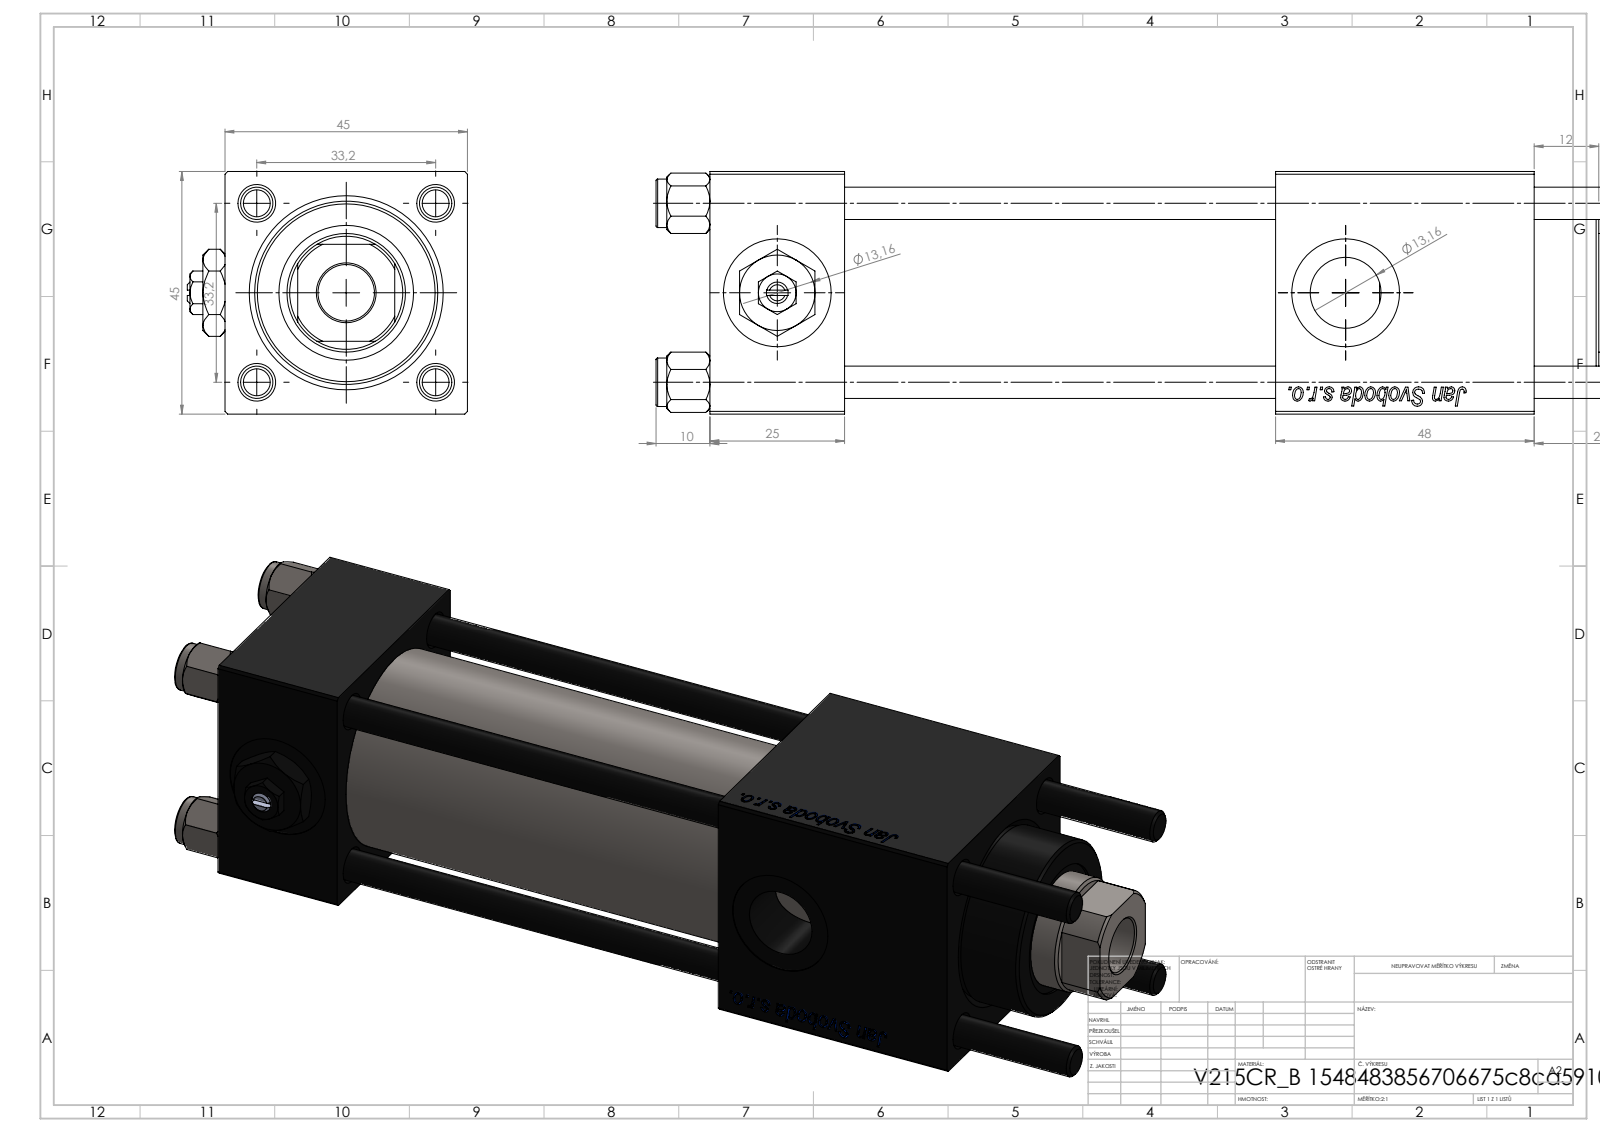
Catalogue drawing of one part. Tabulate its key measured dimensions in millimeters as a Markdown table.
| quantity | value |
| --- | --- |
| part name | V215CR_B_TYCINKA; V215CR_B-1; Zatka_pro_OIL_PORT; NUT_M5_B (+2 more) |
| STEP written by | SolidWorks 2019 (CONFIG_CONTROL_DESIGN) |
| units | millimeters |
| bodies | 12 solids, 1208 faces (454 planar, 84 cylindrical, 670 other) |
| overall size | 188 × 52 × 45 |
| volume | 238 178 mm³ |
| surface area | 88 801 mm² |
| round holes (diameter × count) | 6 × 4, 7 × 2, 13.16 × 2, 20 × 2, 10.5 × 1, 22 × 1, 24 × 1, 25 × 1, 32 × 1, 33 × 1 |
| round bosses / shafts (diameter × count) | 9 × 4, 38 × 1, 34 × 1 |
| partial cylindrical surfaces (radius × count) | 10.5 × 1 |
| main face-to-face distances | 45, 25, 153, 105, 80, 128, 48, 124.3, 99.3, 19.3 |
| hole center spacings | 23.48, 33.2, 46.95, 105.5 |
